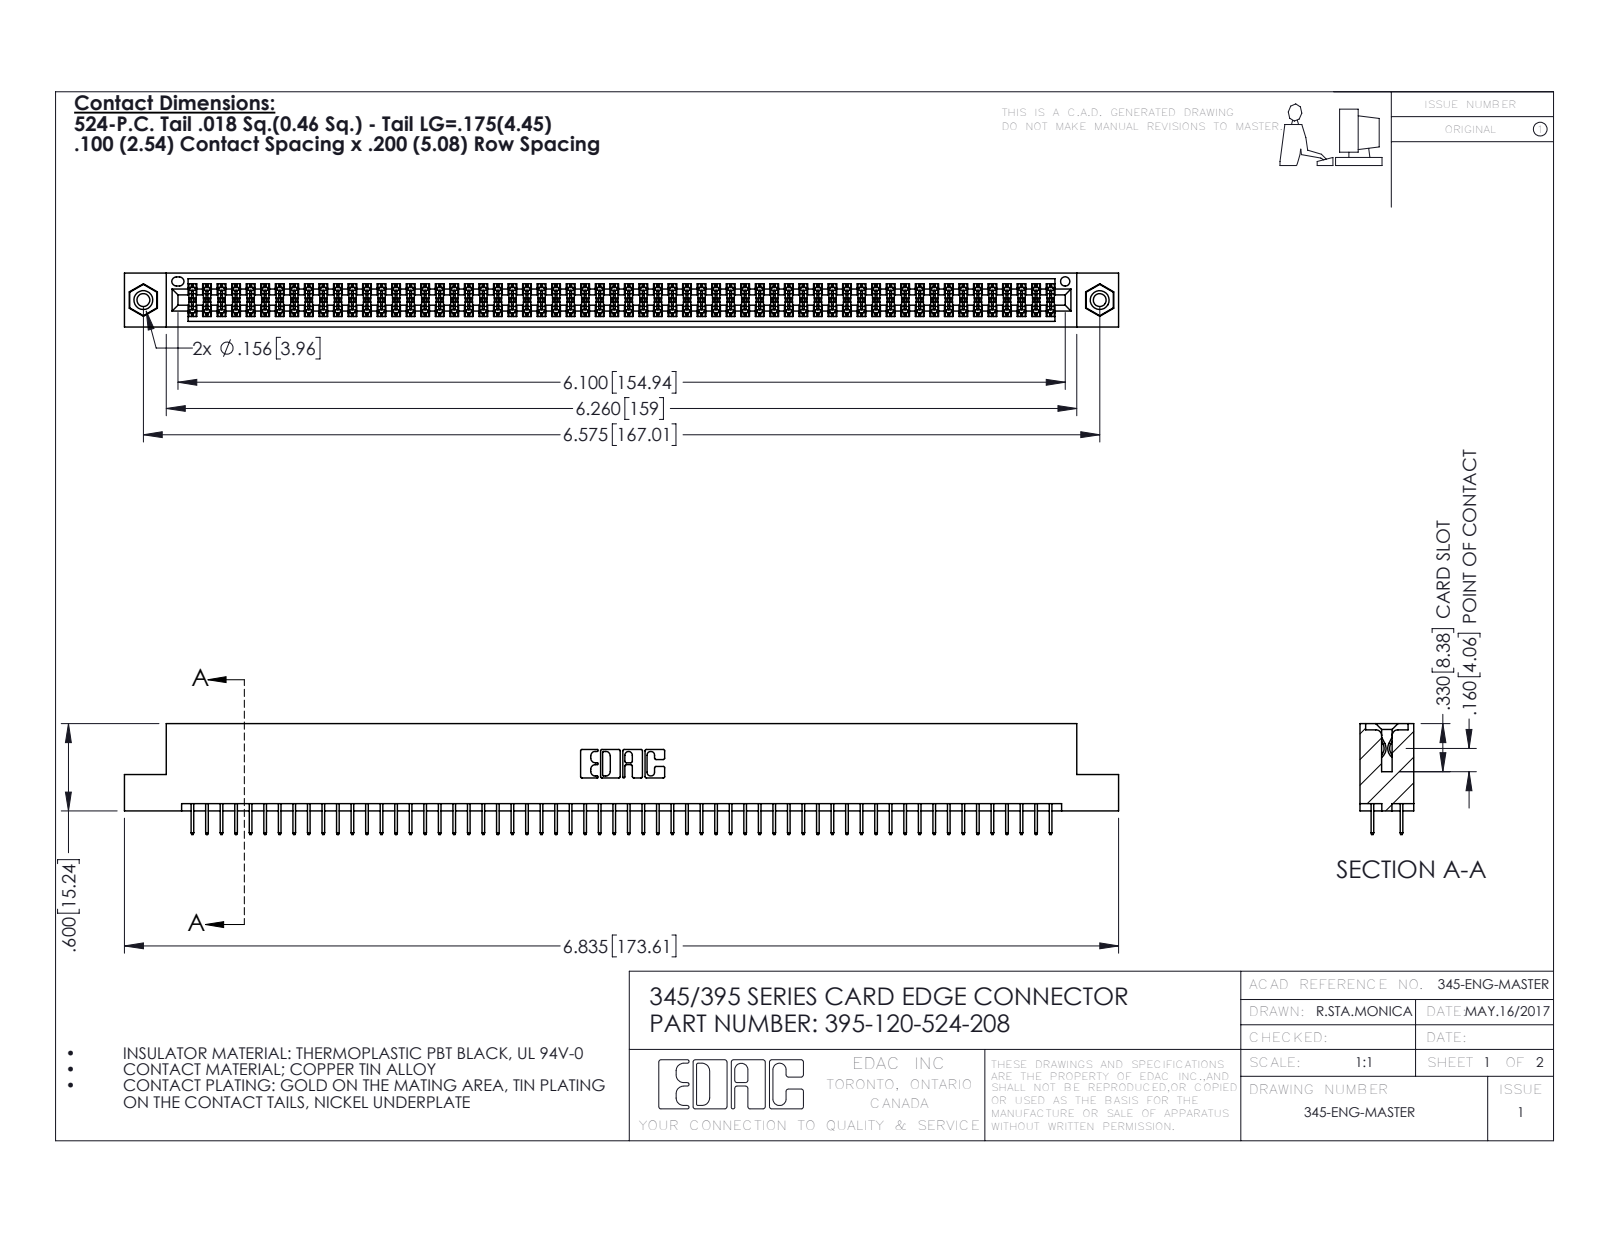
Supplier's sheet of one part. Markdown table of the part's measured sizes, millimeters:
| quantity | value |
| --- | --- |
| part name | 345-292-001_345-293-124; 345-250-001_345-250-003-102; 345 Part_Flush Mounting Lugs - 0.156 Dia-TI; 395-120-524-208 |
| STEP written by | SolidWorks 2016 (CONFIG_CONTROL_DESIGN) |
| units | millimeters |
| bodies | 123 solids, 6666 faces (4792 planar, 1858 cylindrical, 16 other) |
| overall size | 173.6 × 19.4 × 9.4 |
| volume | 16 850 mm³ |
| surface area | 24 780 mm² |
| round holes (diameter × count) | 2.3 × 2, 3.2 × 2, 4 × 2, 1.6 × 1 |
| round bosses / shafts (diameter × count) | 3.9 × 2 |
| partial cylindrical surfaces (radius × count) | 0.2 × 180, 0.3 × 22, 0.2 × 6, 0.8 × 6, 0.7 × 3, 0.4 × 2, 0.5 × 2, 0.6 × 2 |
| main face-to-face distances | 1.8, 7.6, 5.1, 9.4, 2.5, 6.9, 0.6, 5.7, 1.8, 4.4 |
| hole center spacings | 6.9, 161, 167 |
